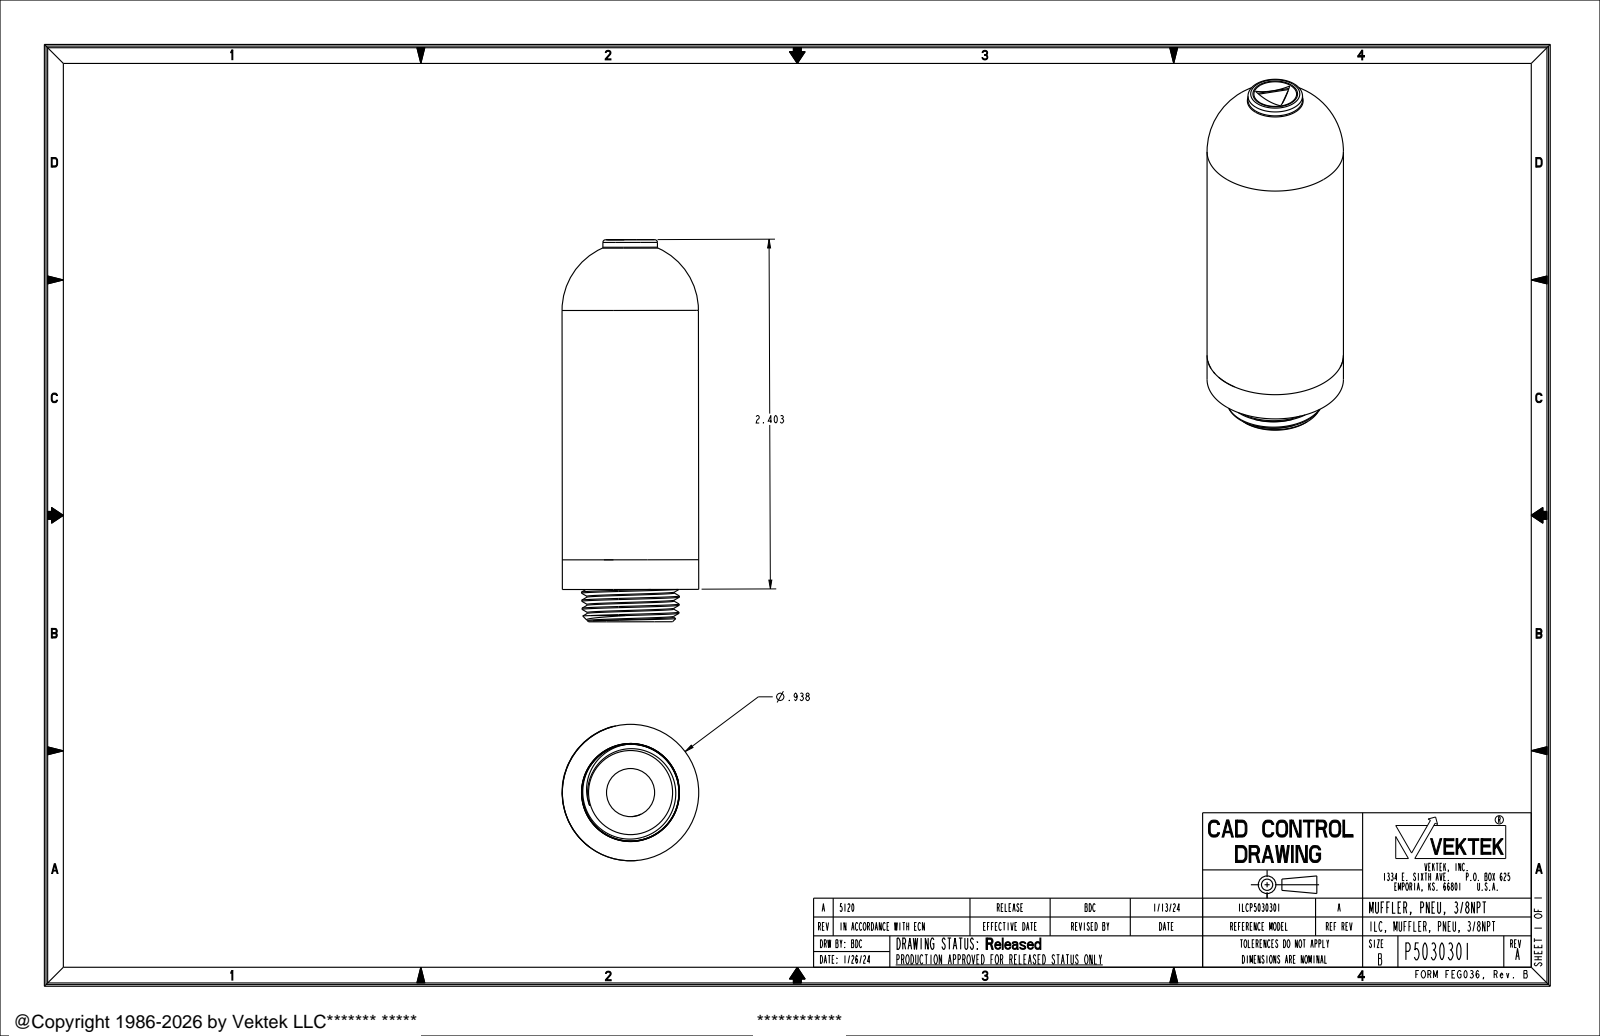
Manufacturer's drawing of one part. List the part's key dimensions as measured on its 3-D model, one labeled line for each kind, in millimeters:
Part name (STEP PRODUCT): ILCP5030301
STEP written by: CREO PARAMETRIC BY PTC INC, 2021164 (AUTOMOTIVE_DESIGN)
Units: millimetres
Bodies: 1 solid, 43 faces (9 planar, 11 cylindrical, 23 other)
Overall size (bounding box): 66.7 × 23.8 × 23.8
Volume: 7 000 mm³ · Surface area: 9 716 mm²
Round holes (diameter × count): ⌀8.4 ×1, ⌀21.9 ×1
Round bosses / shafts (diameter × count): ⌀23.8 ×1, ⌀9.5 ×1
Partial cylindrical surfaces — rounded edges, fillets, slot ends (radius × count): R0.1 ×3
Main face-to-face distances: 6.1, 5.6, 11.8, 64.2, 58.5, 52.4, 66, 60.3, 54.2, 1.8
